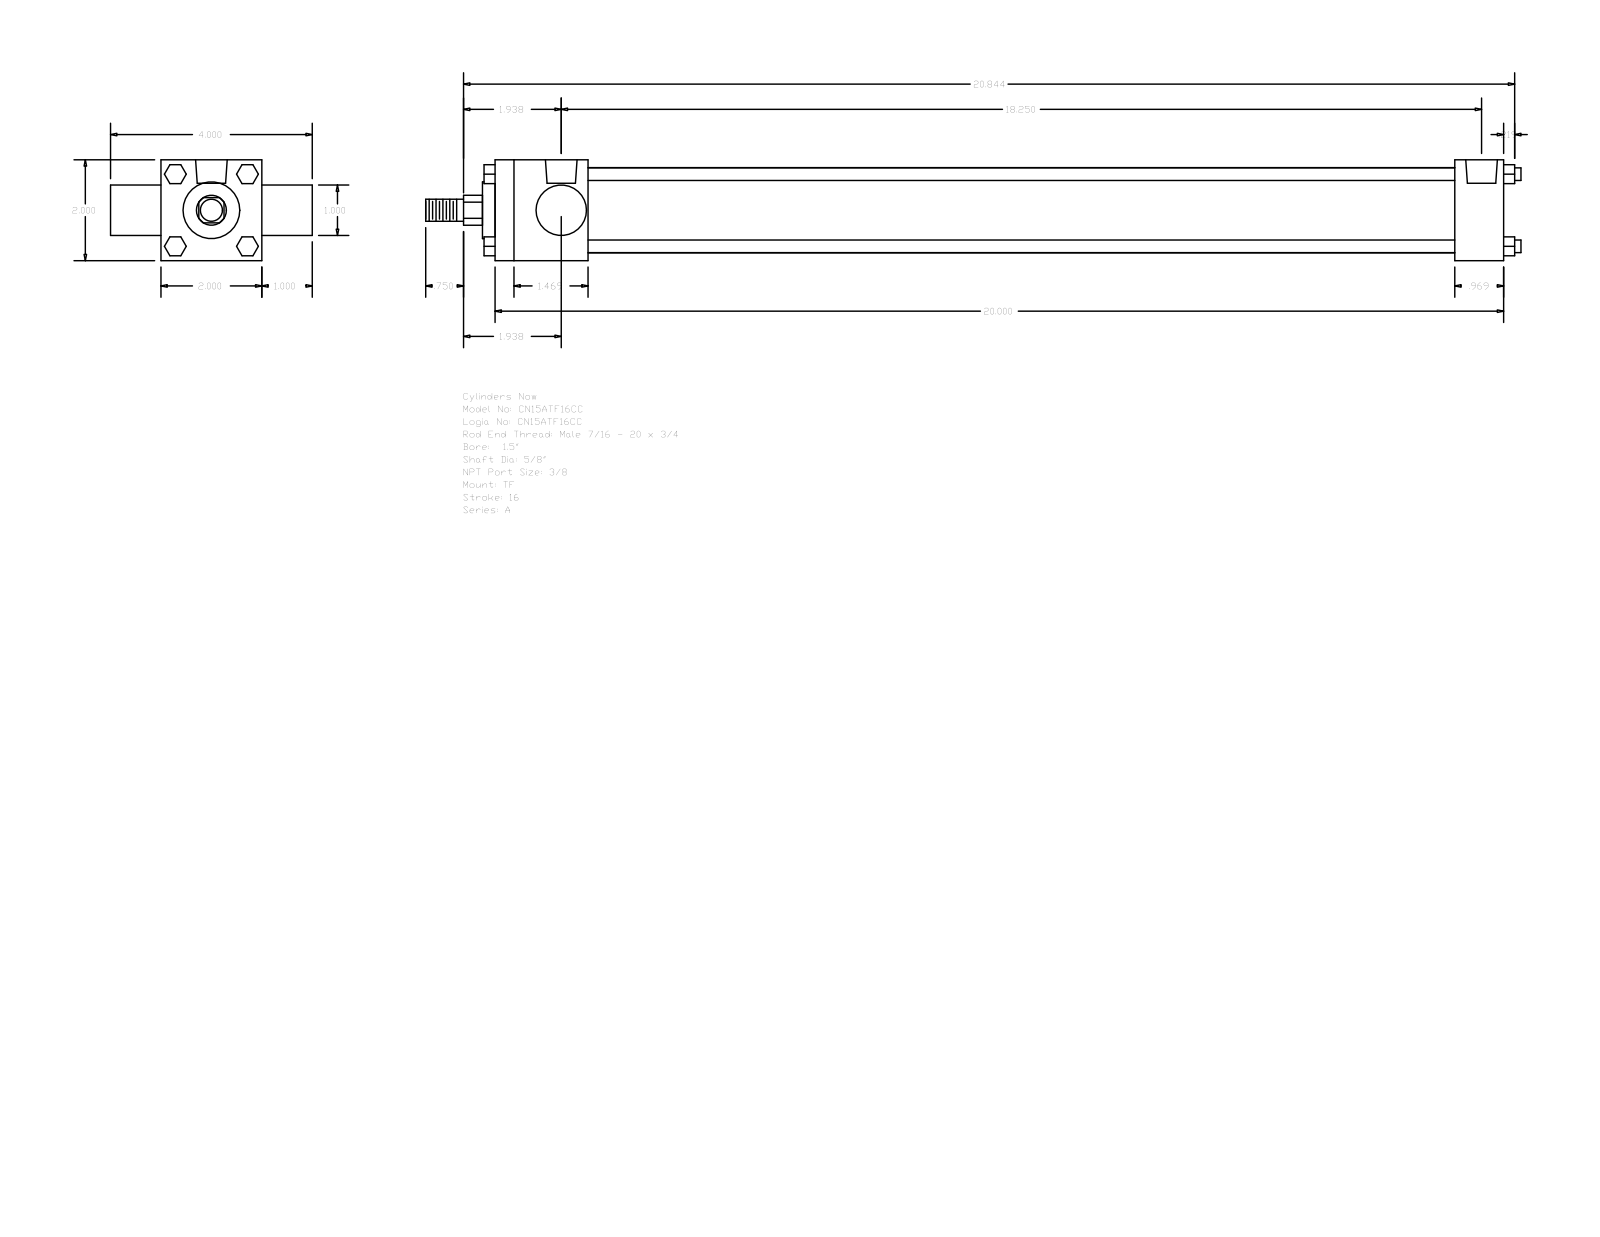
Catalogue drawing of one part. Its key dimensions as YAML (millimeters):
part_name: "A_TF__0150_0.625"
step_written_by: "GSSL Pune (CONFIG_CONTROL_DESIGN)"
units: millimeters
bodies: {solids: 0, faces: 120, planar: 92, cylindrical: 28, other: 0}
overall_size: [551.66, 101.6, 50.8]
round_holes:
  - {diameter: 5.56, count: 3}
  - {diameter: 15.93, count: 2}
round_bosses_or_shafts:
  - {diameter: 6.35, count: 4}
  - {diameter: 42.93, count: 1}
  - {diameter: 28.57, count: 1}
  - {diameter: 25.4, count: 1}
  - {diameter: 15.88, count: 1}
  - {diameter: 11.11, count: 1}
partial_cylinders:
  - {radius: 7.54, count: 1}
face_to_face_distances: [50.8, 508, 25.4, 76.2, 46.83, 483.39, 436.56, 461.17, 24.61, 101.6]
hole_center_spacings: [3.97, 459.58, 455.61, 463.55]
